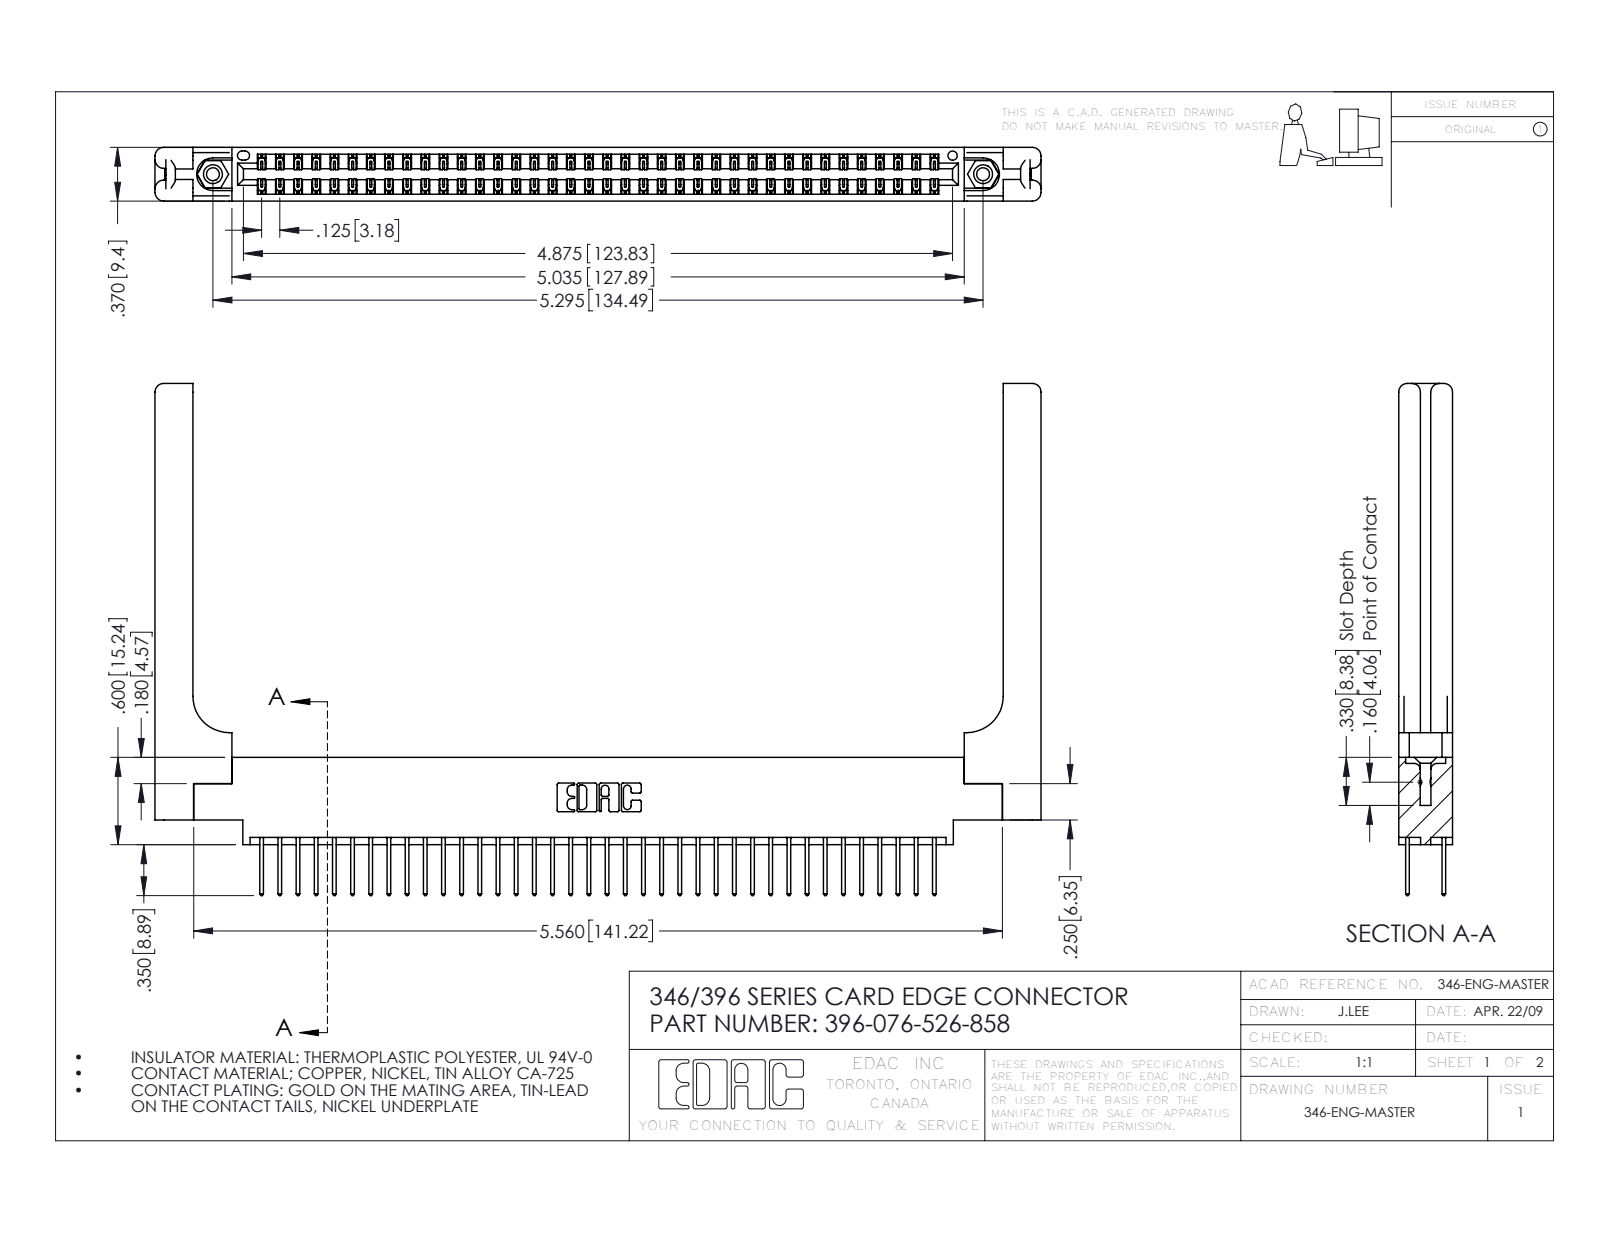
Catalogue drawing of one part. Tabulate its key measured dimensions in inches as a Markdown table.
| quantity | value |
| --- | --- |
| part name | 345-250-001_345-250-001-102; 396-076-526-858; 345-292-001_345-293-126; 346-220-058_345-220-058 (+1 more) |
| STEP written by | SolidWorks 2016 (CONFIG_CONTROL_DESIGN) |
| units | inches |
| bodies | 81 solids, 4334 faces (2888 planar, 1386 cylindrical, 60 other) |
| overall size | 6.091 × 3.52 × 0.37 |
| volume | 1.374 in³ |
| surface area | 40.77 in² |
| round holes (diameter × count) | 0.089 × 2, 0.125 × 2, 0.156 × 2, 0.064 × 1 |
| round bosses / shafts (diameter × count) | 0.155 × 2 |
| partial cylindrical surfaces (radius × count) | 0.006 × 114, 0.01 × 76, 0.01 × 22, 0.06 × 16, 0.007 × 6, 0.031 × 6, 0.026 × 3, 0.014 × 2 |
| main face-to-face distances | 0.37, 0.048, 0.322, 0.072, 0.25, 0.025, 0.148, 0.15, 0.298, 0.275 |
| hole center spacings | 0.246, 5.086, 5.295 |
